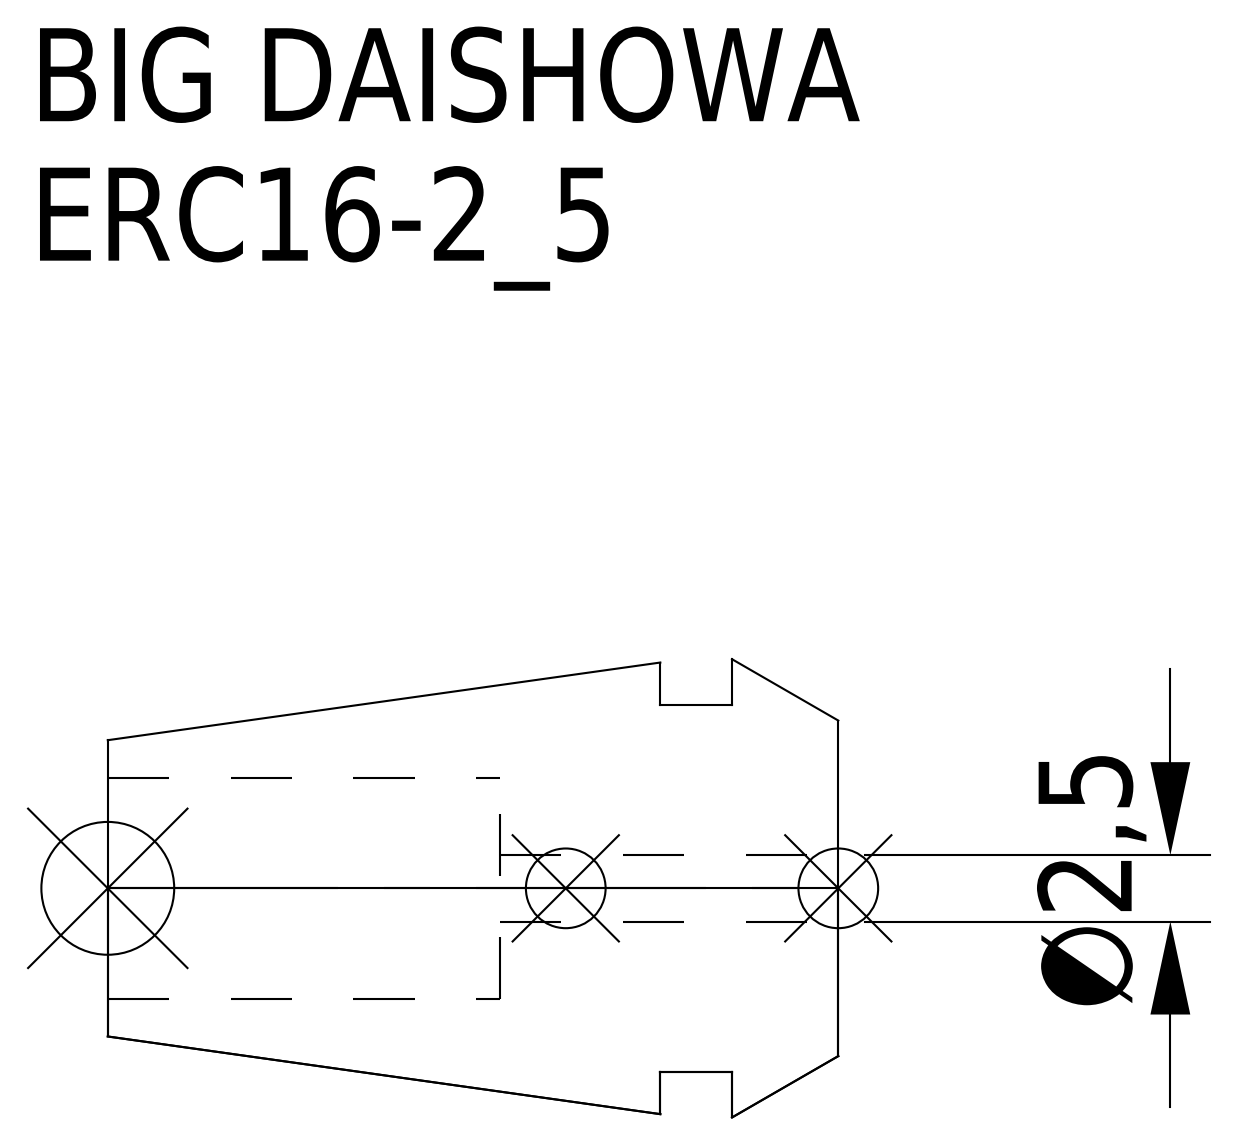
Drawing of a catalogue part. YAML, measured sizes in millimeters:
part_name: "ERC16-2_5"
step_written_by: "CREO PARAMETRIC BY PTC INC, 2016380 (AUTOMOTIVE_DESIGN)"
units: millimeters
bodies: {solids: 1, faces: 15, planar: 5, cylindrical: 6, other: 4}
overall_size: [27.5, 17.25, 17.25]
volume: 3533
surface_area: 2123
round_holes:
  - {diameter: 2.5, count: 1}
  - {diameter: 8.3, count: 1}
round_bosses_or_shafts:
  - {diameter: 13.8, count: 1}
face_to_face_distances: [4, 6.7, 2.7, 12.73, 8.73, 6.03, 27.5, 23.5, 20.8, 14.77]
